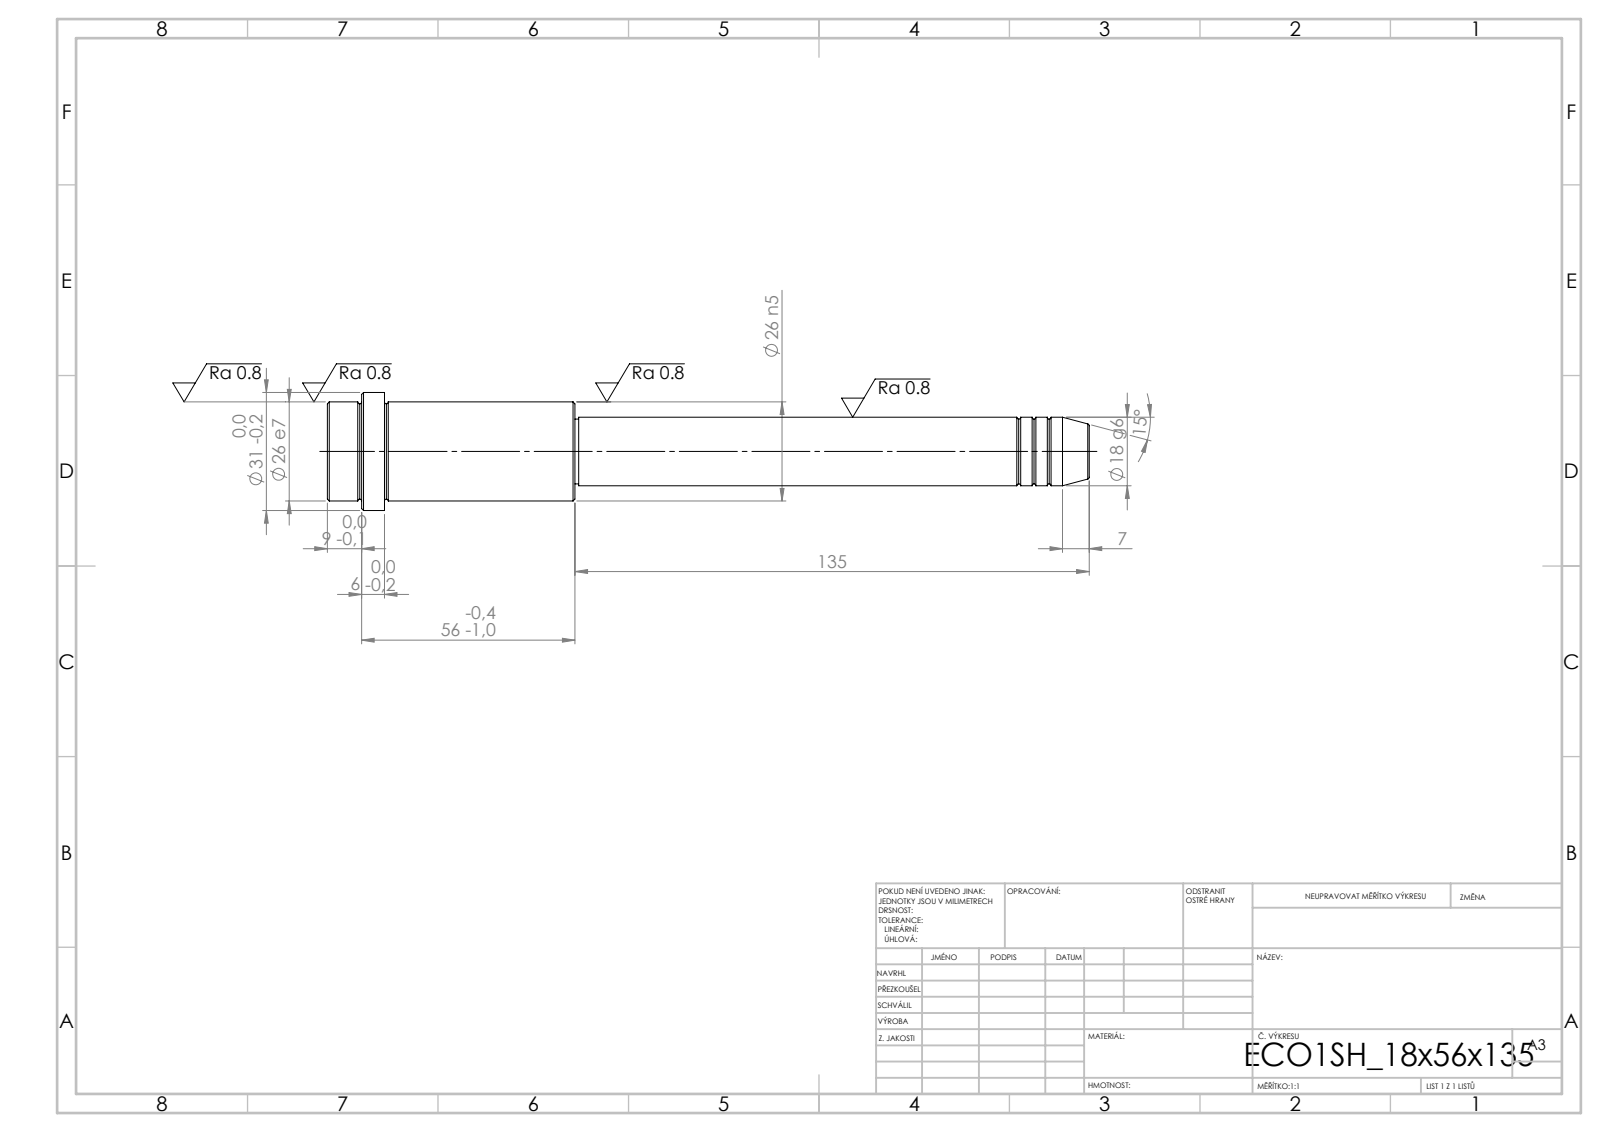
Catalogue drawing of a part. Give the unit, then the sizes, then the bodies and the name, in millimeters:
Units: millimetres
Overall size (bounding box): 200 × 31 × 31
Round bosses / shafts (diameter × count): ⌀31 ×1, ⌀26 ×1, ⌀18 ×1, ⌀17 ×1
Main face-to-face distances: 65, 50, 15, 56, 6, 9, 135, 185, 191, 200
Volume: 69 672 mm³ · Surface area: 14 567 mm²
Bodies: 1 solid, 52 faces (6 planar, 16 cylindrical, 30 other)
STEP written by: SolidWorks 2019 (CONFIG_CONTROL_DESIGN)
